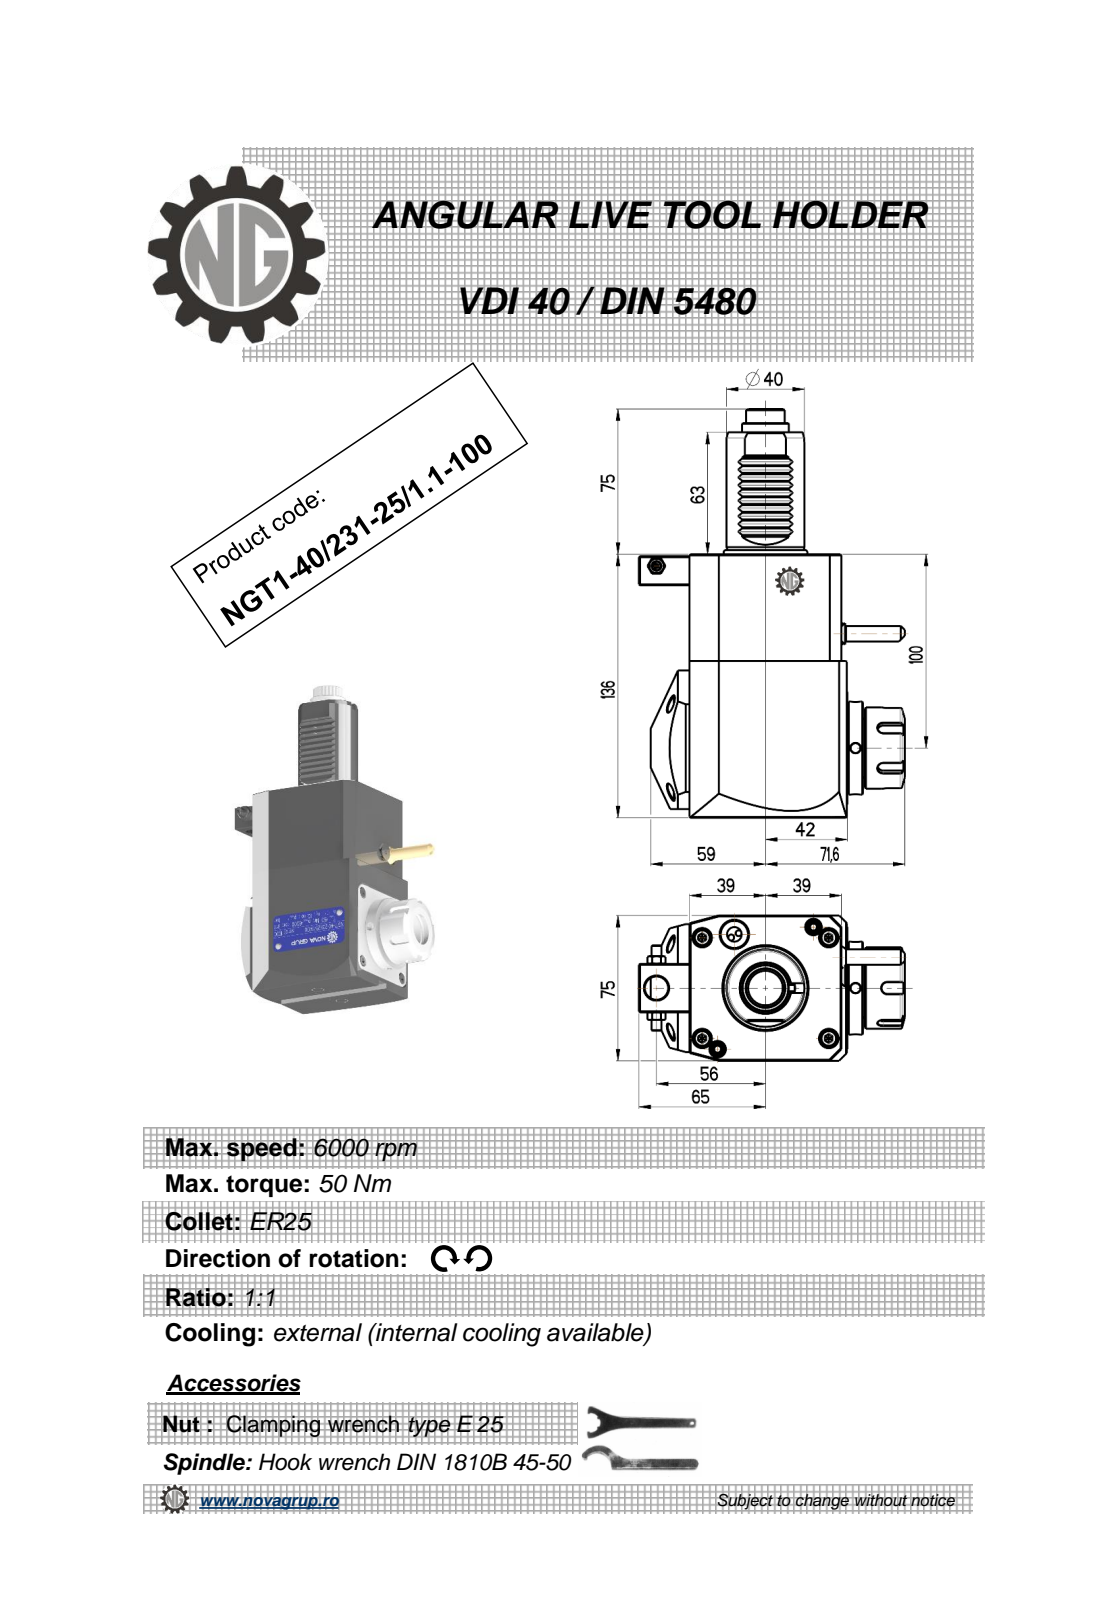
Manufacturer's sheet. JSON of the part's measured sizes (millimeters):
{"part_name": "NGT1_40_231_25_1_1_100", "step_written_by": "PRO/ENGINEER BY PARAMETRIC TECHNOLOGY CORPORATION, 2010280 (CONFIG_CONTROL_DESIGN)", "units": "millimeters", "bodies": {"solids": 1, "faces": 555, "planar": 194, "cylindrical": 185, "other": 176}, "overall_size": [211, 136.6, 76.6], "volume_mm3": 980195, "surface_area_mm2": 75757, "round_holes": [[5, 3], [3, 1], [4.2, 1], [9.5, 1], [12, 1], [20.3, 1]], "round_bosses_or_shafts": [[48, 1], [42, 1], [40, 1], [37.5, 1], [33, 1], [24, 1], [11.2, 1], [8.96, 1]], "partial_cylinders_radius": [[2.08, 48], [0.26, 12], [0.3, 10], [0.22, 6], [3, 5], [9.08, 1], [9.92, 1], [15, 1]], "face_to_face_distances": [75, 136, 78, 81, 3, 80.8, 2.8, 7.5, 0.5, 11], "hole_center_spacings": [36.22, 61.13, 91.5, 102.25, 138.89]}
